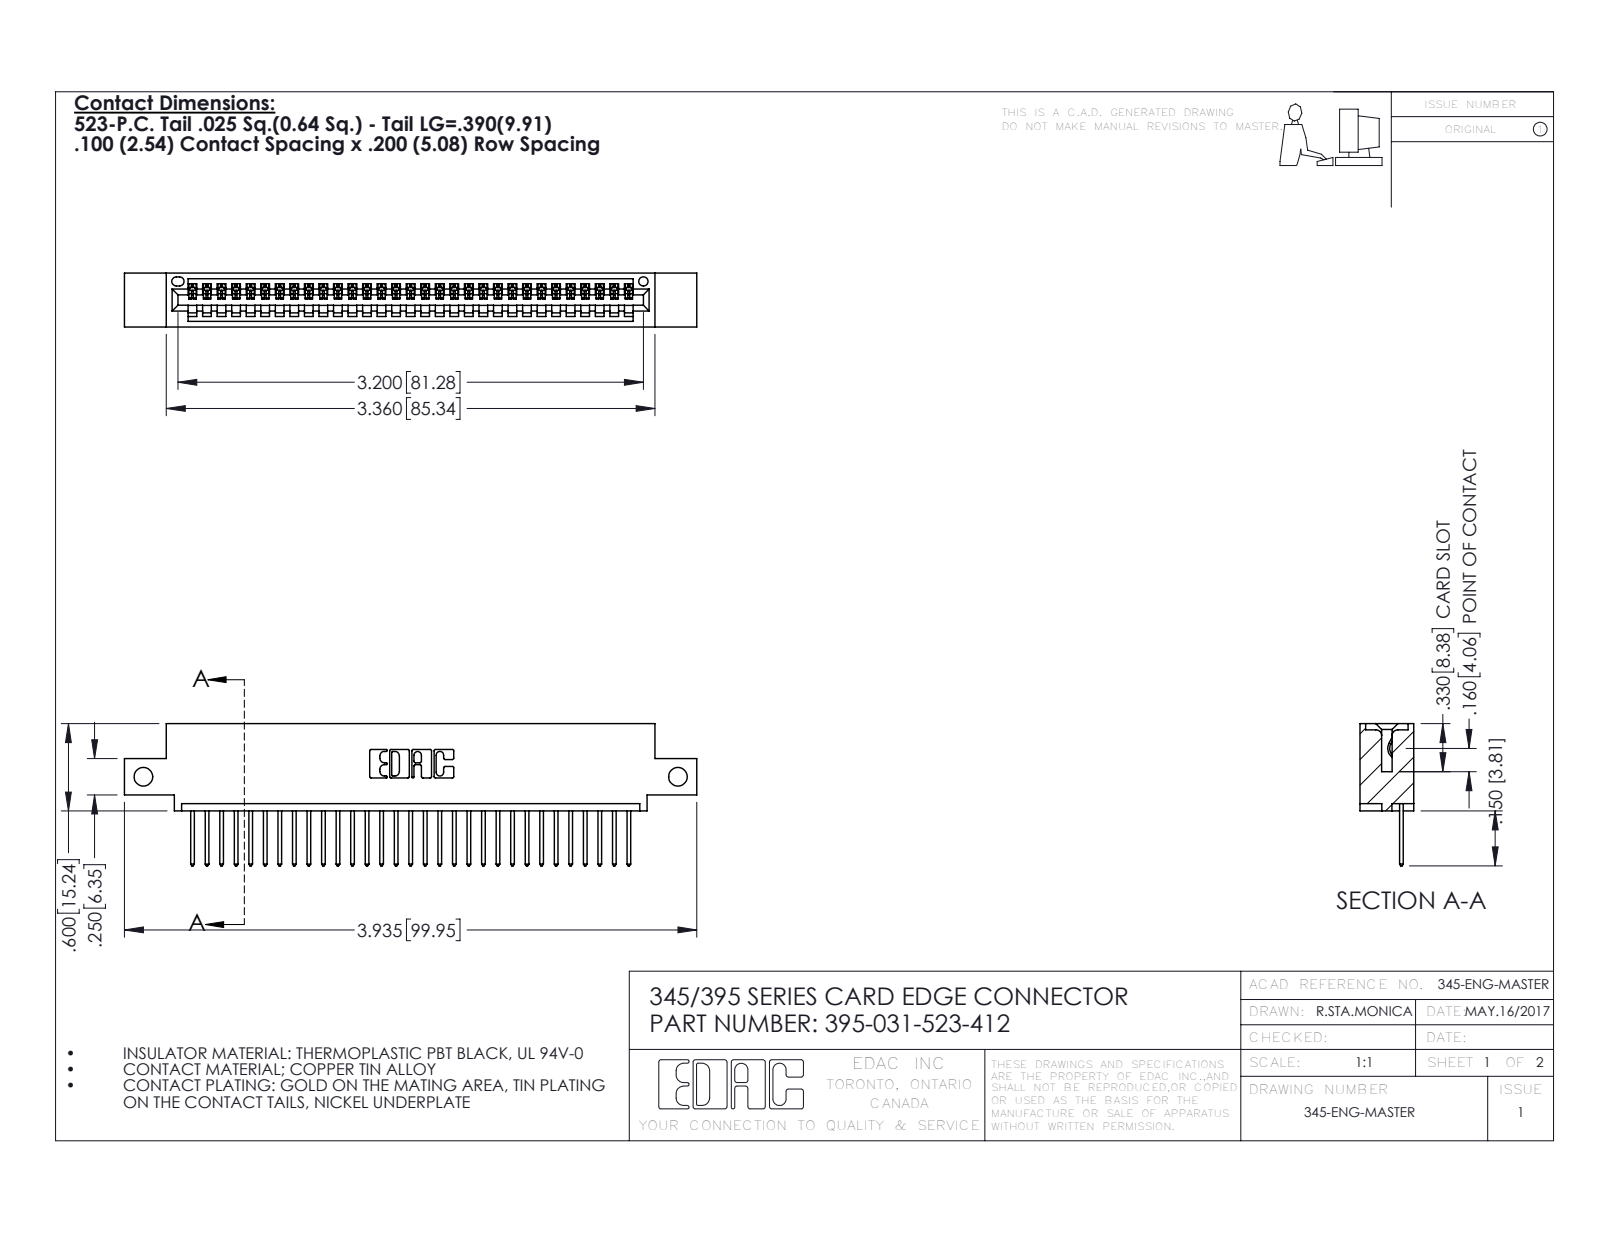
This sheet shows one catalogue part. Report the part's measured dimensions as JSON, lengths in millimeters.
{"part_name": "345 Part_0.110 Offset - Side Mount; 395-031-523-412; 345-292-001_345-293-123", "step_written_by": "SolidWorks 2016 (CONFIG_CONTROL_DESIGN)", "units": "millimeters", "bodies": {"solids": 32, "faces": 1928, "planar": 1324, "cylindrical": 604, "other": 0}, "overall_size": [99.9, 24.8, 9.4], "volume_mm3": 9230, "surface_area_mm2": 12090, "round_holes": [[3.3, 2], [1.6, 1]], "partial_cylinders_radius": [[0.2, 62], [0.3, 62], [0.3, 22], [0.2, 6], [0.8, 6], [0.7, 3], [0.8, 2], [1, 2]], "face_to_face_distances": [7.6, 1.8, 9.4, 5.1, 2.5, 6.9, 0.6, 5.7, 3.8, 1.8], "hole_center_spacings": [93.3]}
